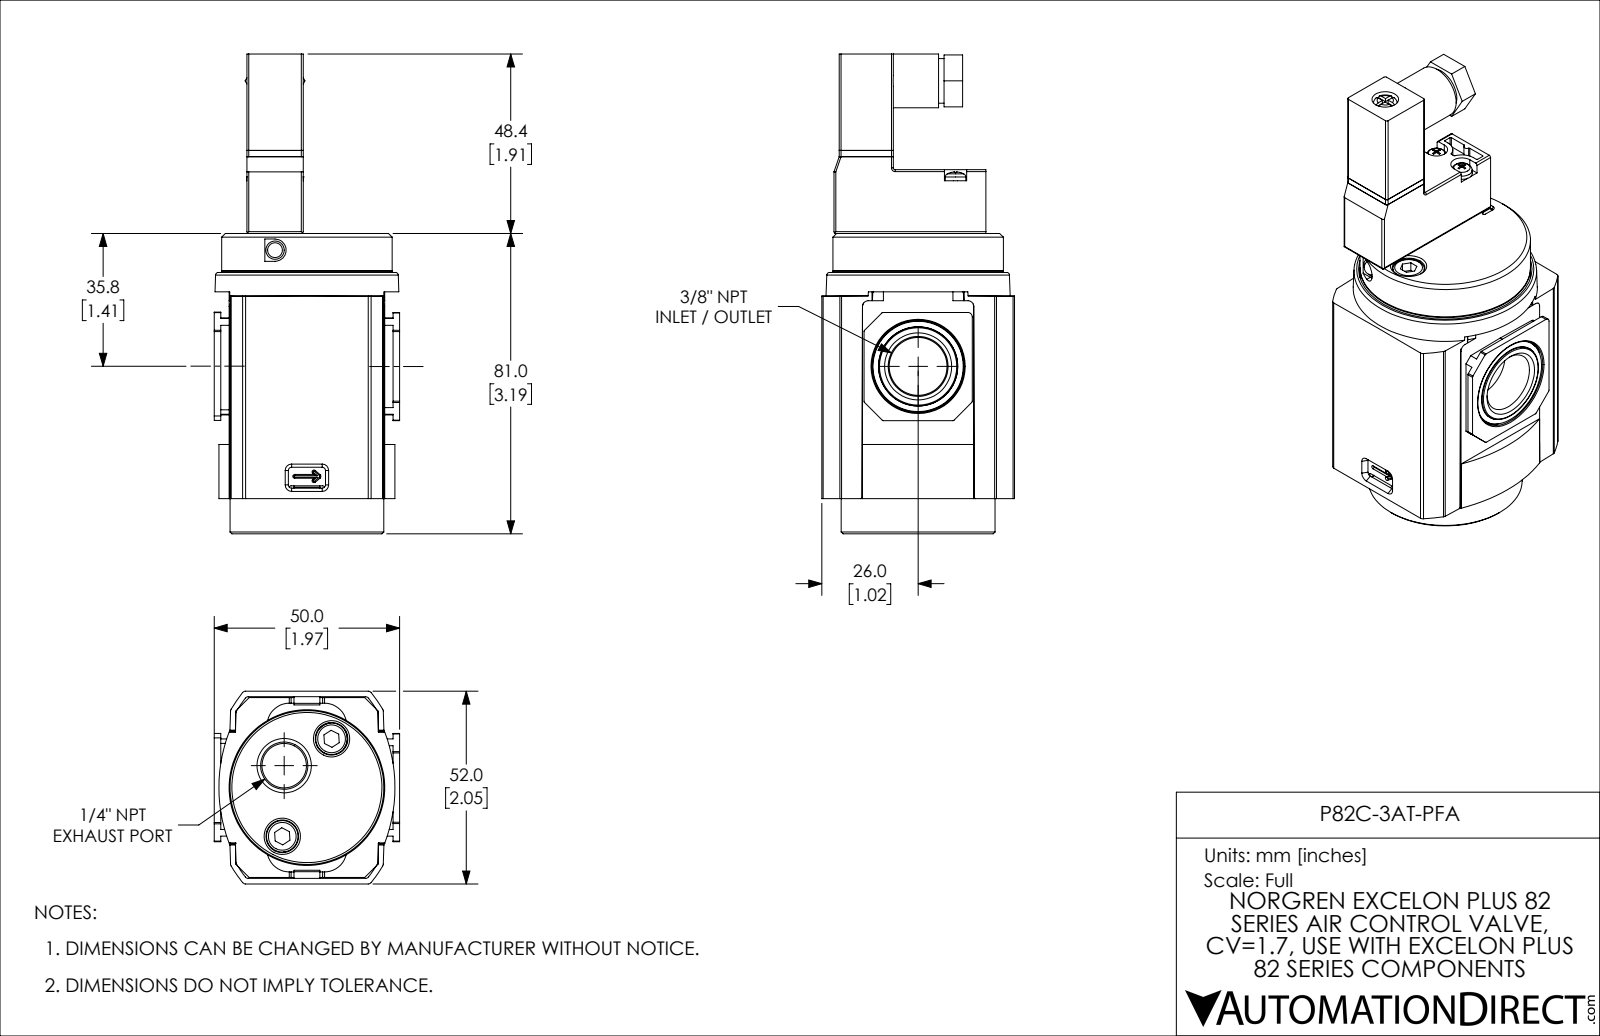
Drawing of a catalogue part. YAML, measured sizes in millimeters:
part_name: "P82C-3AT-PFA"
step_written_by: "SolidWorks 2021 (CONFIG_CONTROL_DESIGN)"
units: millimeters
bodies: {solids: 7, faces: 785, planar: 350, cylindrical: 226, other: 209}
overall_size: [129.4, 52, 50]
volume: 174465
surface_area: 57740
round_holes:
  - {diameter: 4.13, count: 4}
  - {diameter: 5.3, count: 4}
  - {diameter: 8.8, count: 4}
  - {diameter: 1.5, count: 3}
  - {diameter: 2.46, count: 3}
  - {diameter: 0.8, count: 2}
  - {diameter: 3.1, count: 2}
  - {diameter: 8.5, count: 2}
  - {diameter: 3.8, count: 1}
  - {diameter: 6.8, count: 1}
  - {diameter: 7.2, count: 1}
  - {diameter: 40, count: 1}
round_bosses_or_shafts:
  - {diameter: 5, count: 4}
  - {diameter: 8.5, count: 2}
  - {diameter: 3, count: 2}
  - {diameter: 46, count: 1}
  - {diameter: 41.5, count: 1}
  - {diameter: 39.8, count: 1}
  - {diameter: 37, count: 1}
  - {diameter: 14.5, count: 1}
partial_cylinders:
  - {radius: 0.5, count: 37}
  - {radius: 0.25, count: 18}
  - {radius: 1, count: 16}
  - {radius: 1.2, count: 4}
  - {radius: 3, count: 4}
  - {radius: 6, count: 4}
  - {radius: 0.1, count: 2}
  - {radius: 1.25, count: 2}
face_to_face_distances: [1.75, 1.5, 50.5, 50.25, 48.75, 10, 49.5, 59.5, 52, 49]
hole_center_spacings: [3.8, 5.05, 5.41, 7.11, 14.74, 16.69, 24.88, 2.55]
